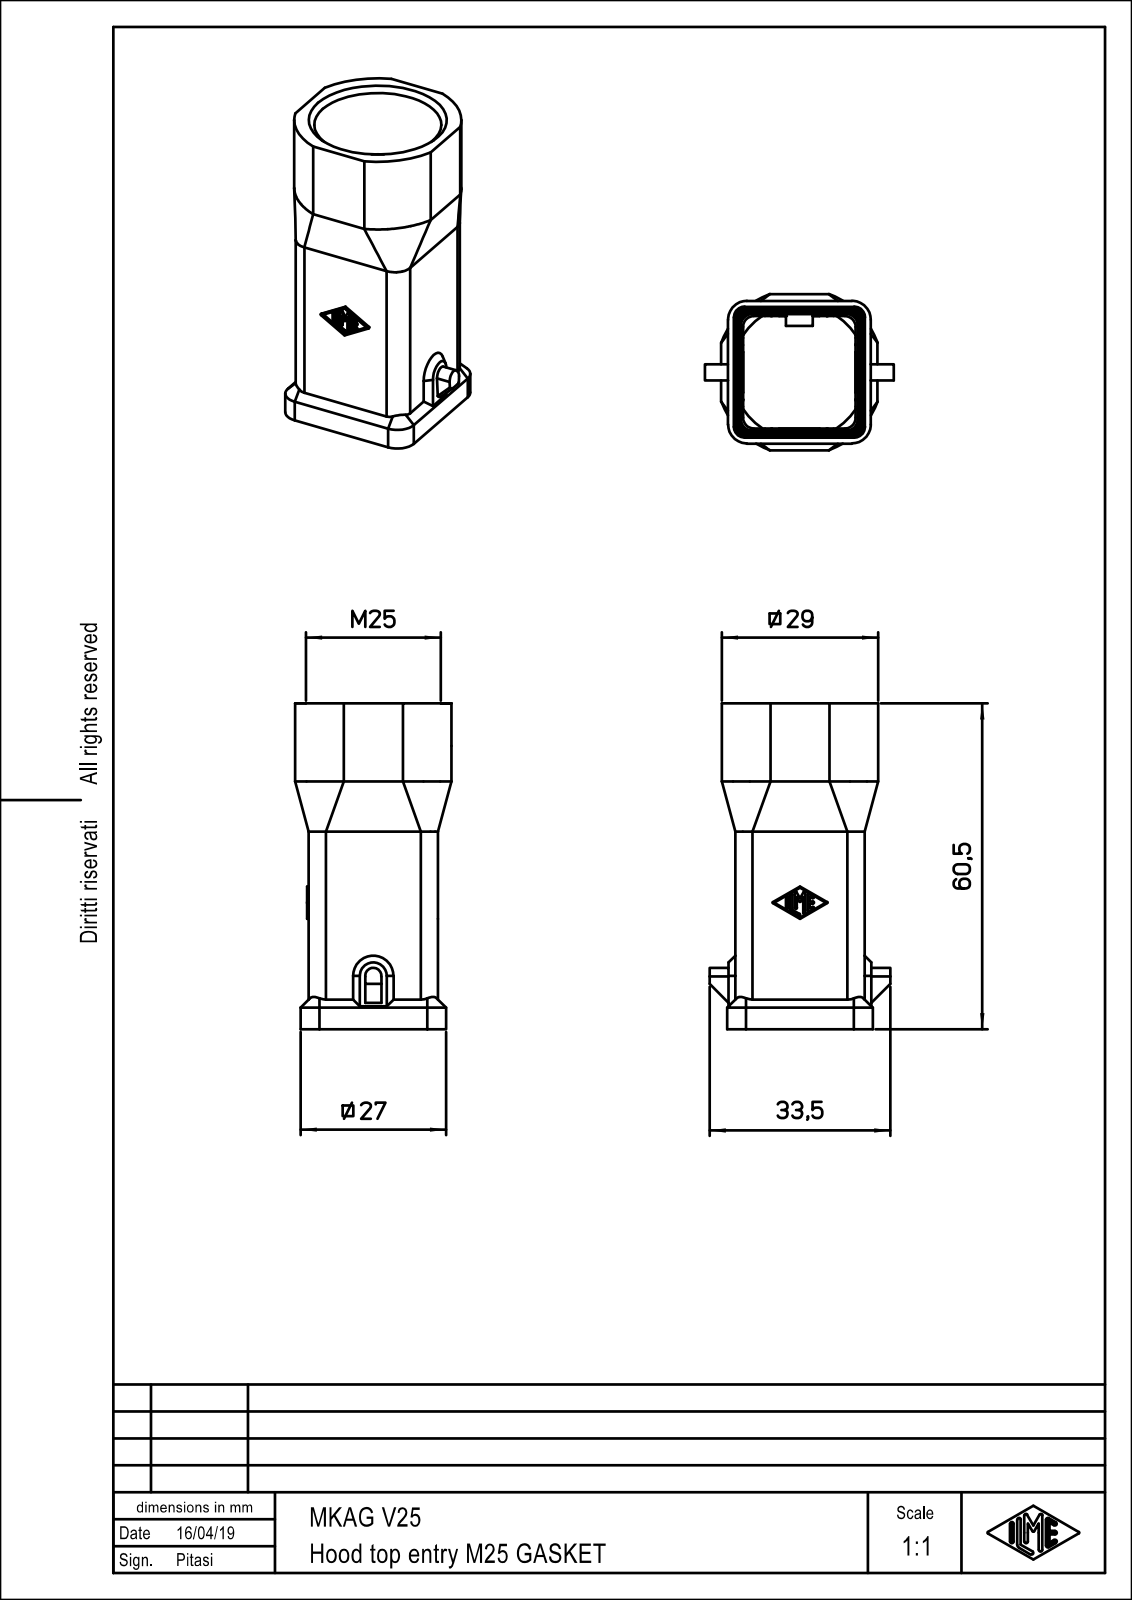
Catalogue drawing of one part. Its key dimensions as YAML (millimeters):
part_name: "MKAG_V25_54215; MKAG_V25.stp"
step_written_by: "PTC Creo Elements/Direct Modeling 19.0E 27-Jun-2016 (C) Parametric Technology GmbH (AUTOMOTIVE_DESIGN)"
units: millimeters
bodies: {solids: 1, faces: 301, planar: 226, cylindrical: 60, other: 15}
overall_size: [60.5, 33.5, 29.3]
volume: 11070
surface_area: 12044
round_holes:
  - {diameter: 3.2, count: 1}
  - {diameter: 7, count: 1}
  - {diameter: 20, count: 1}
  - {diameter: 23.6, count: 1}
partial_cylinders:
  - {radius: 2, count: 16}
  - {radius: 0.2, count: 11}
  - {radius: 3.2, count: 4}
  - {radius: 3.5, count: 4}
  - {radius: 0.1, count: 3}
  - {radius: 0.16, count: 2}
  - {radius: 1.75, count: 2}
  - {radius: 2.5, count: 2}
face_to_face_distances: [1.2, 22.8, 21.6, 24, 1.5, 2.5, 26.5, 24.3, 3.7, 25.3]
